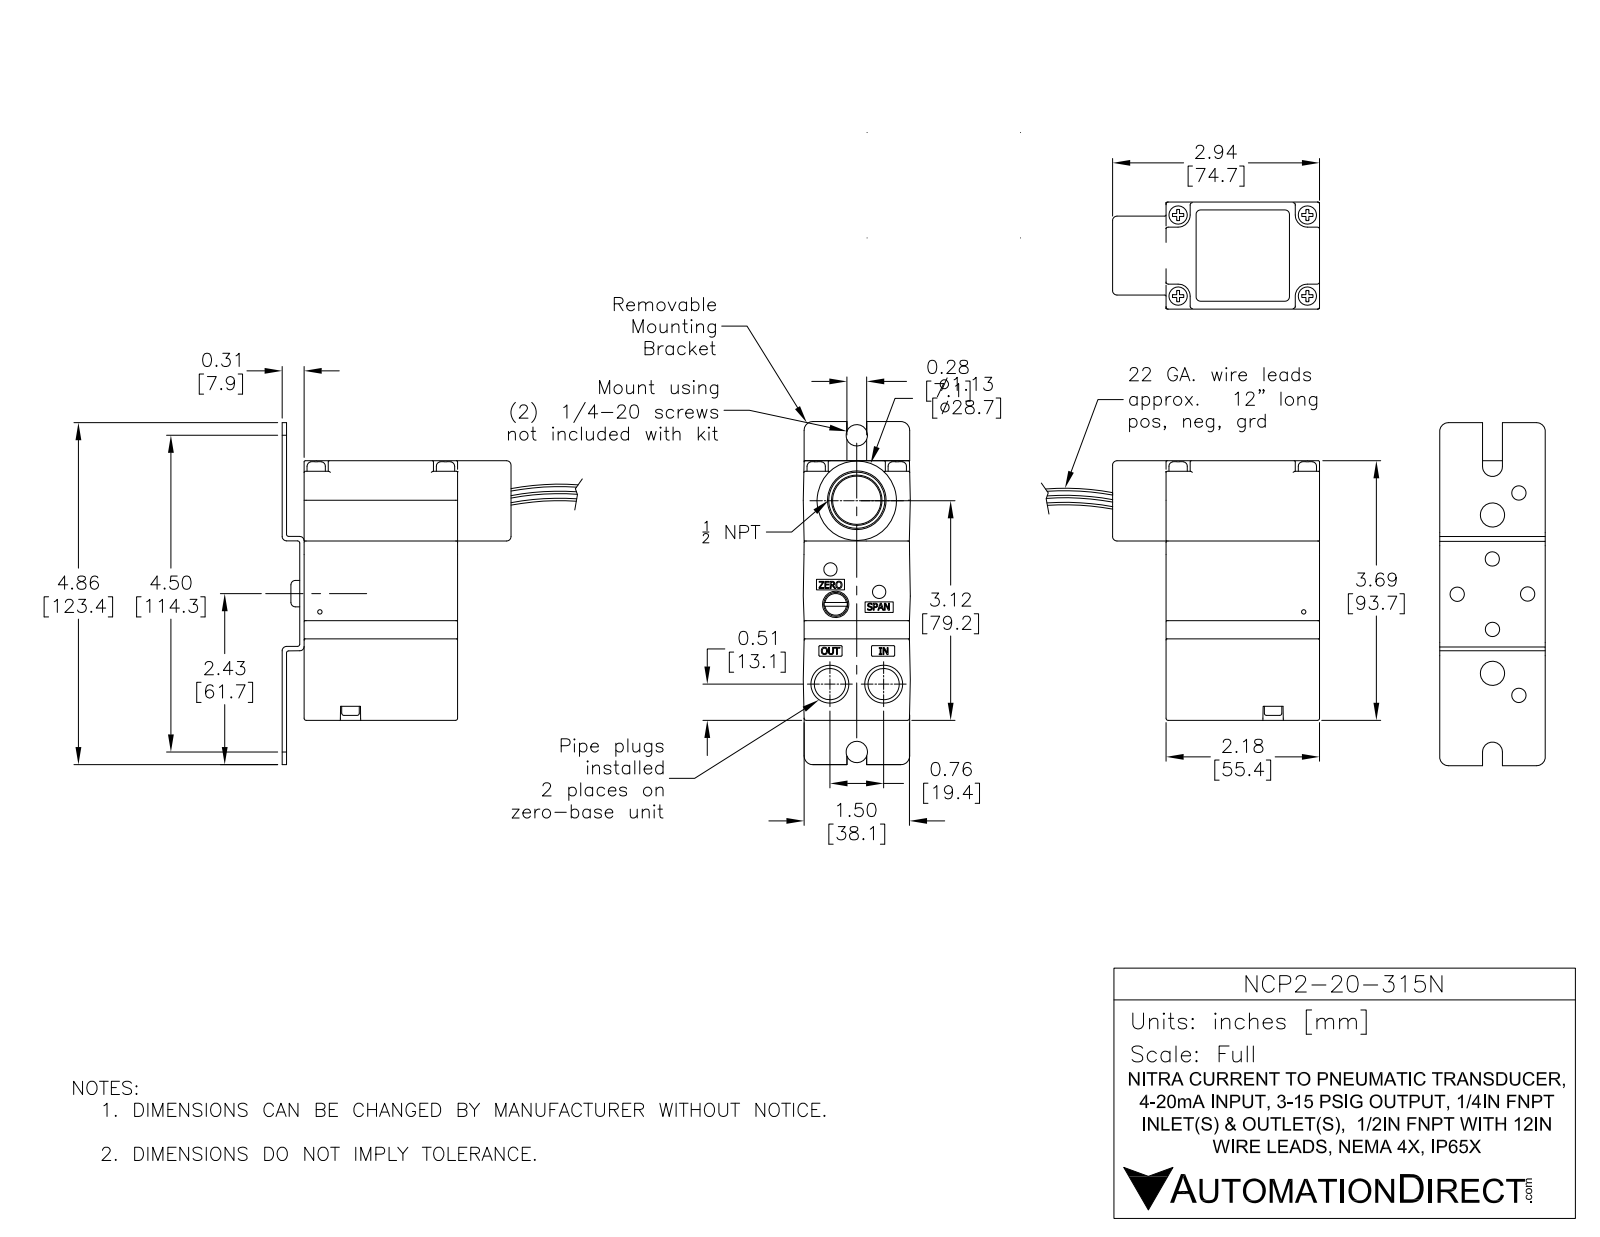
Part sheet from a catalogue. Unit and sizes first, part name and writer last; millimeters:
Units: millimetres
Overall size (bounding box): 124.1 × 83.35 × 39.12
Round holes (diameter × count): ⌀5.16 ×6, ⌀3.37 ×3, ⌀3.18 ×2, ⌀3.3 ×2, ⌀4.8 ×2, ⌀8.73 ×2, ⌀11.38 ×2, ⌀1.59 ×1, ⌀3.17 ×1, ⌀7.37 ×1, ⌀17.48 ×1, ⌀20.07 ×1
Round bosses / shafts (diameter × count): ⌀6.6 ×4, ⌀6.35 ×3, ⌀7.49 ×2, ⌀28.95 ×1, ⌀16.18 ×1, ⌀11.43 ×1, ⌀8.66 ×1
Partial cylindrical surfaces — rounded edges, fillets, slot ends (radius × count): R0.76 ×56, R0.5 ×17, R0.4 ×8, R1.59 ×8, R3.17 ×8, R1.47 ×6, R1.25 ×4, R1.27 ×4
Main face-to-face distances: 1.59, 6.75, 7.03, 8.62, 55.55, 37.35, 38.74, 1.39, 55.54, 62.57
Hole centre spacings: 25.4, 12.4, 15.87, 17.74, 17.94, 17.96, 18.41, 18.78
Volume: 189 475 mm³ · Surface area: 49 479 mm²
Bodies: 4 solids, 1003 faces (537 planar, 291 cylindrical, 175 other)
Part name (STEP PRODUCT): NCP2-20-315N
STEP written by: SolidWorks 2016 (AUTOMOTIVE_DESIGN)
